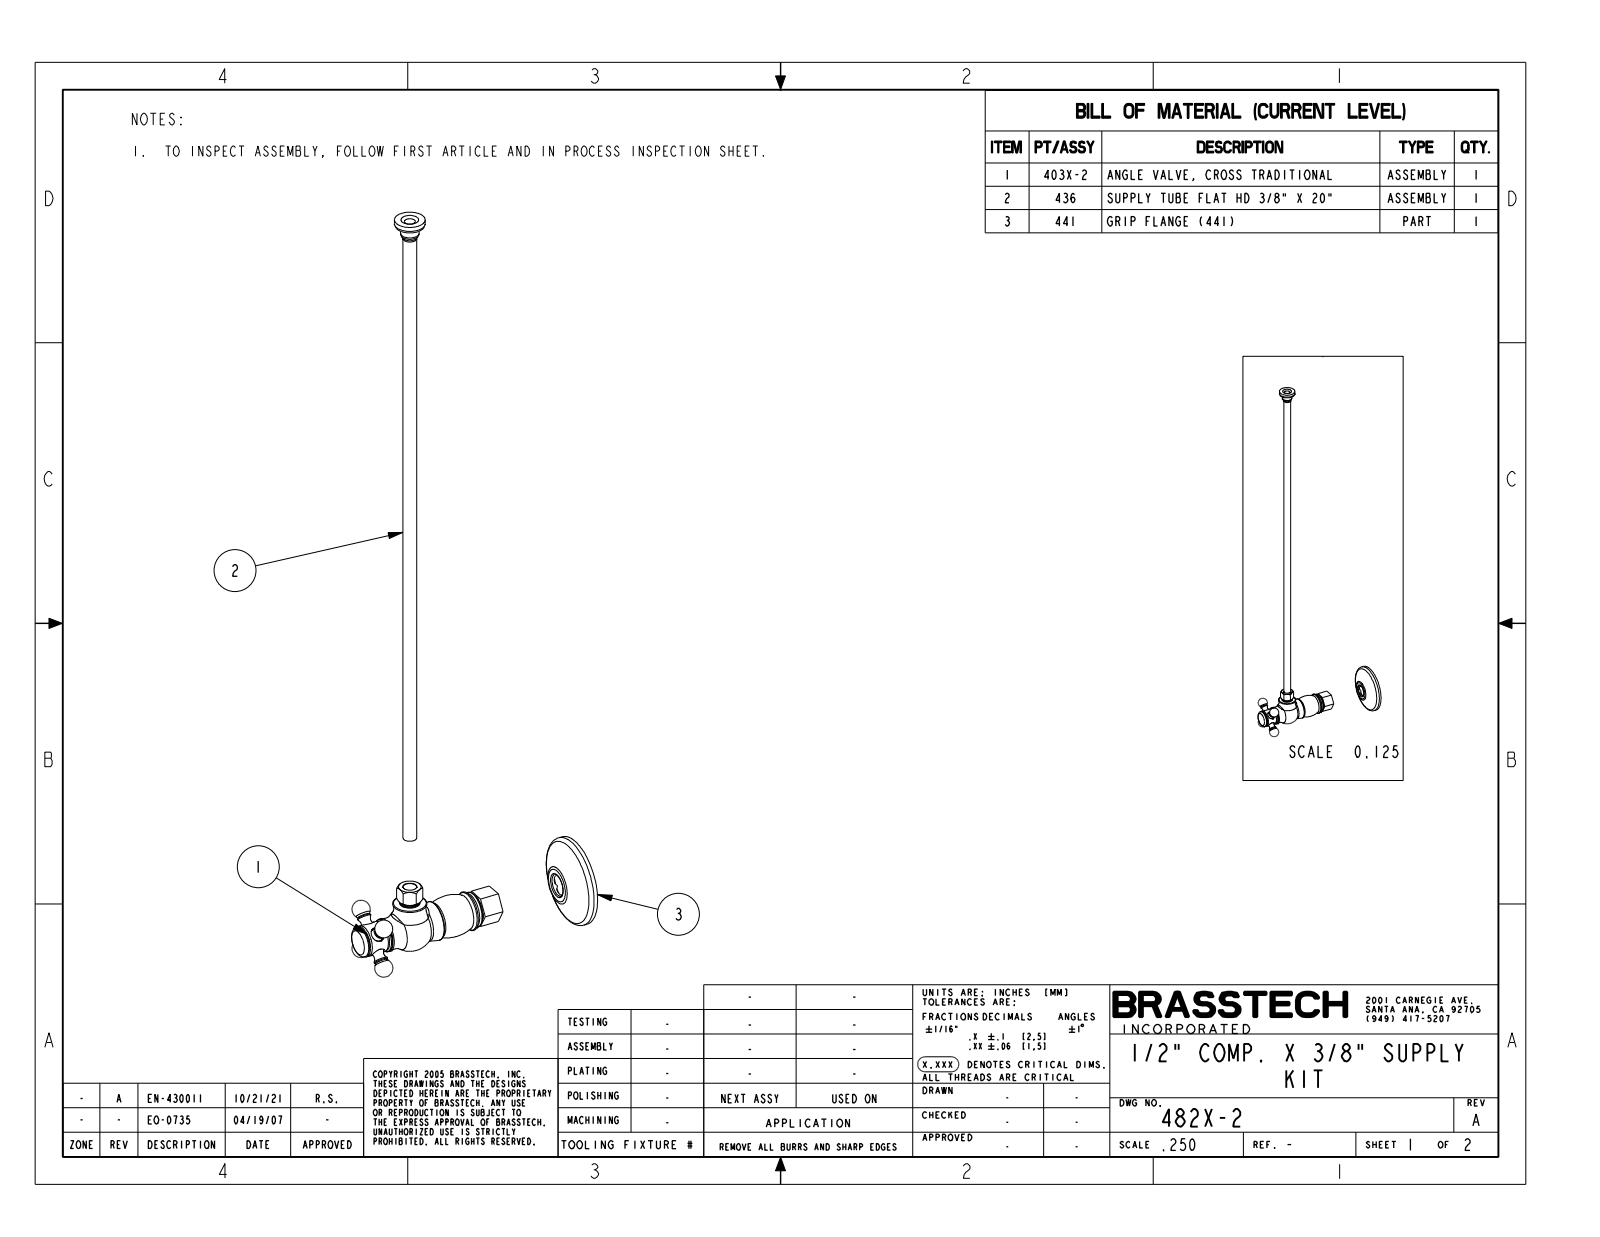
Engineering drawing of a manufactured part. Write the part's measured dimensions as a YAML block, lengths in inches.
part_name: "482X-2"
step_written_by: "CREO PARAMETRIC BY PTC INC, 2018500 (CONFIG_CONTROL_DESIGN)"
units: inches
bodies: {solids: 7, faces: 1253, planar: 294, cylindrical: 468, other: 491}
overall_size: [21.615, 6.903, 2.5]
volume: 1.449
surface_area: 157.4
round_holes:
  - {diameter: 0.207, count: 2}
  - {diameter: 0.062, count: 1}
  - {diameter: 0.128, count: 1}
  - {diameter: 0.163, count: 1}
  - {diameter: 0.3, count: 1}
  - {diameter: 0.328, count: 1}
  - {diameter: 0.335, count: 1}
  - {diameter: 0.38, count: 1}
  - {diameter: 0.39, count: 1}
  - {diameter: 0.4, count: 1}
  - {diameter: 0.41, count: 1}
  - {diameter: 0.424, count: 1}
round_bosses_or_shafts:
  - {diameter: 0.392, count: 2}
  - {diameter: 0.25, count: 2}
  - {diameter: 0.18, count: 2}
  - {diameter: 2.5, count: 1}
  - {diameter: 0.906, count: 1}
  - {diameter: 0.885, count: 1}
  - {diameter: 0.876, count: 1}
  - {diameter: 0.87, count: 1}
partial_cylinders:
  - {radius: 0.03, count: 10}
  - {radius: 0.058, count: 5}
  - {radius: 0.04, count: 2}
  - {radius: 0.057, count: 2}
  - {radius: 0.063, count: 2}
  - {radius: 0.08, count: 2}
  - {radius: 0.145, count: 2}
  - {radius: 0.137, count: 1}
face_to_face_distances: [0.875, 0.625, 2.033, 0.343, 2.376, 0.787, 1.13, 3.163, 0.698, 0.185]
hole_center_spacings: [0.228]
